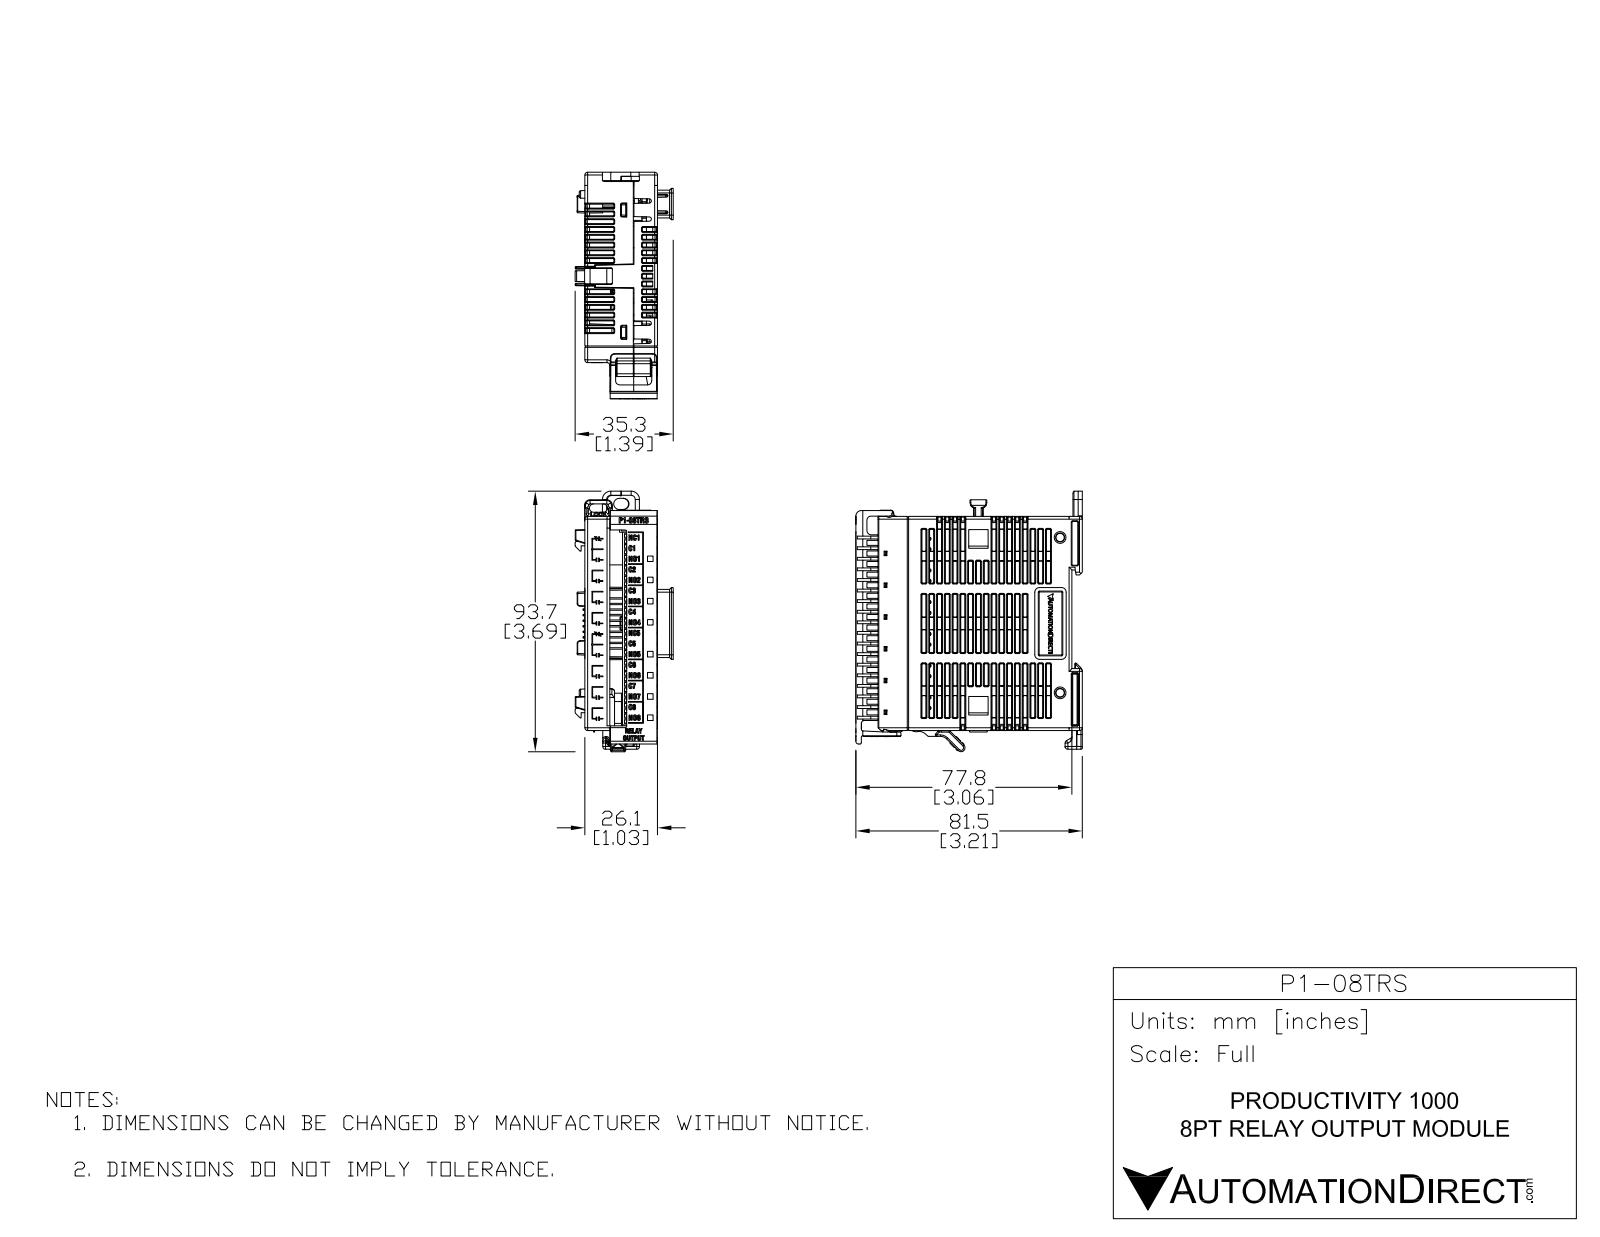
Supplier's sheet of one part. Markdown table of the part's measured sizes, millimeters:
| quantity | value |
| --- | --- |
| part name | P1-08TRS red1 comb 2 fXT w bot clip Comb B ext C coord fXT |
| STEP written by | SolidWorks 2017 (AUTOMOTIVE_DESIGN) |
| units | millimeters |
| bodies | 11 solids, 4611 faces (3052 planar, 734 cylindrical, 825 other) |
| overall size | 93.7 × 81.8 × 35.3 |
| volume | 132 600 mm³ |
| surface area | 37 950 mm² |
| round holes (diameter × count) | 0.3 × 20, 0.6 × 8, 1.2 × 1 |
| round bosses / shafts (diameter × count) | 1.1 × 2, 1.6 × 1 |
| partial cylindrical surfaces (radius × count) | 0.5 × 112, 0.3 × 104, 0.2 × 80, 0.3 × 75, 1 × 70, 1.5 × 13, 2 × 12, 3 × 11 |
| main face-to-face distances | 26.2, 77, 58.9, 75.8, 16.9, 1.7, 2, 24.5, 3.8, 77.7 |
| hole center spacings | 2, 2.8, 4, 4.5, 6, 6.3, 8, 8.3 |
